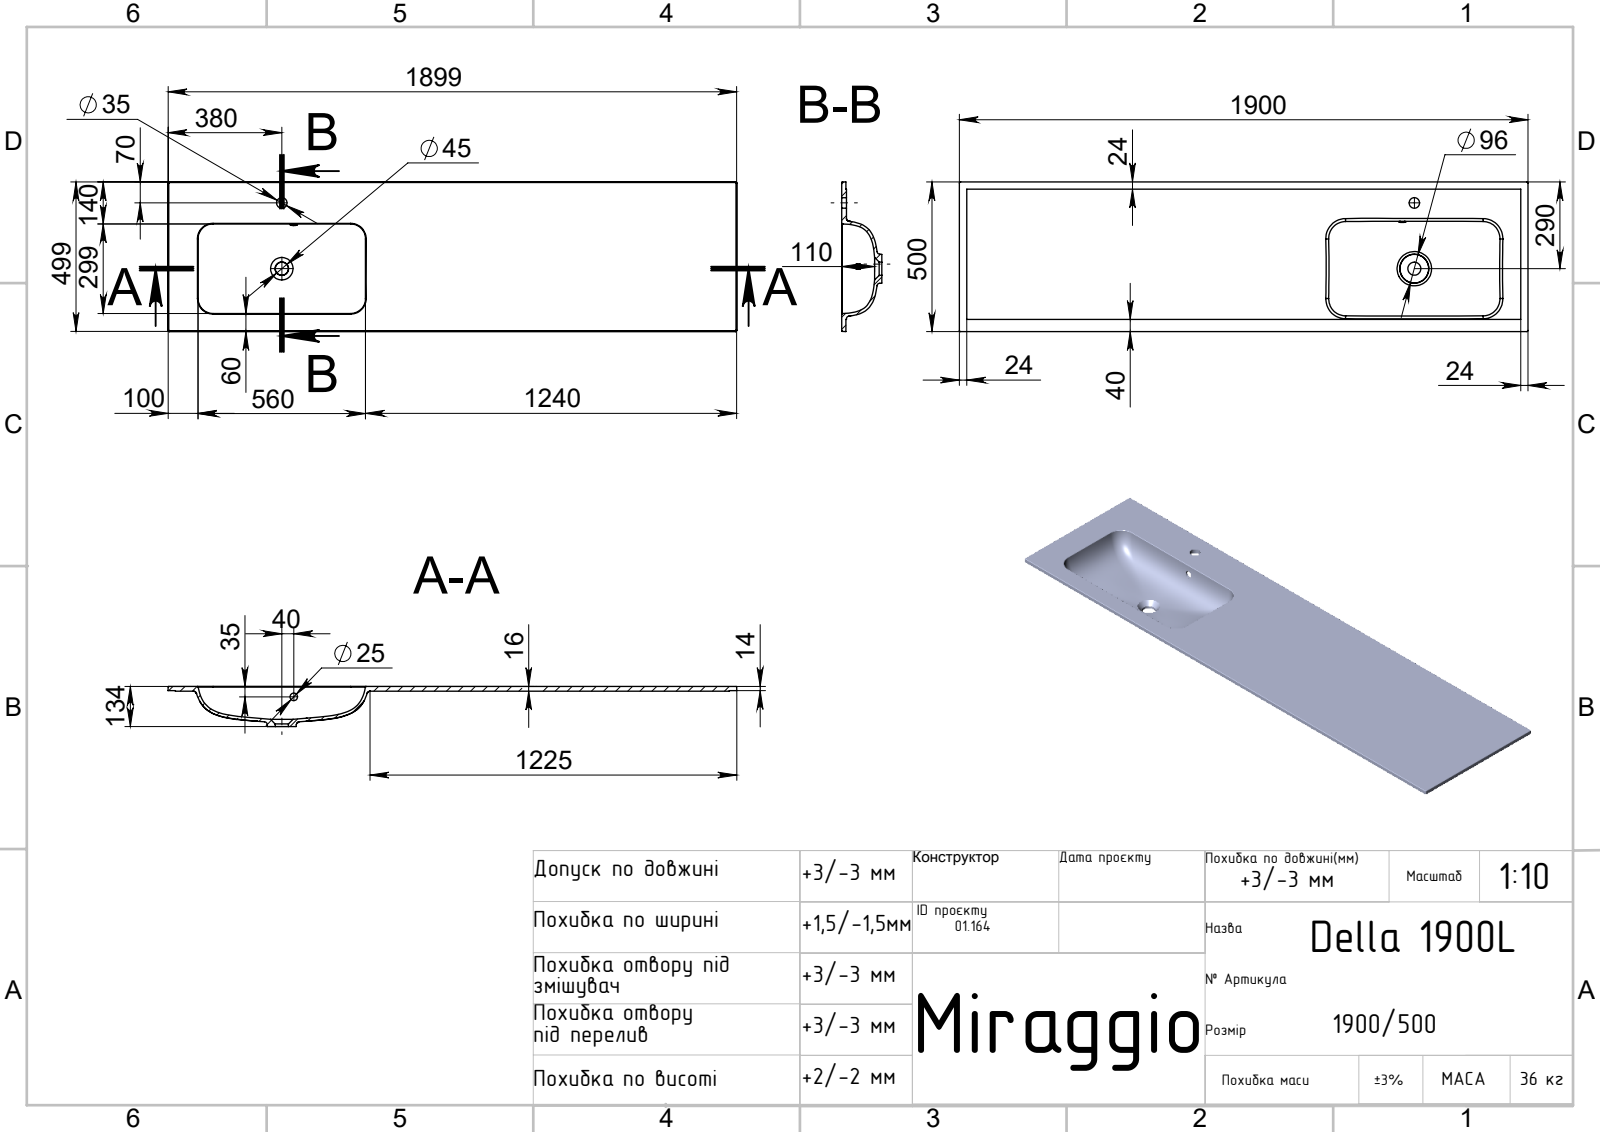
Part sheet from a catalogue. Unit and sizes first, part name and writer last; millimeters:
Units: millimetres
Overall size (bounding box): 1900 × 500 × 134
Round holes (diameter × count): ⌀25 ×1, ⌀35 ×1
Partial cylindrical surfaces — rounded edges, fillets, slot ends (radius × count): R2 ×4, R4 ×4
Main face-to-face distances: 16, 2, 14, 118, 120, 134, 461.26, 1861.26
Volume: 14 930 000 mm³ · Surface area: 2 143 000 mm²
Bodies: 1 solid, 57 faces (12 planar, 12 cylindrical, 33 other)
Part name (STEP PRODUCT): Della 1900L
STEP written by: SolidWorks 2020 (AUTOMOTIVE_DESIGN)
